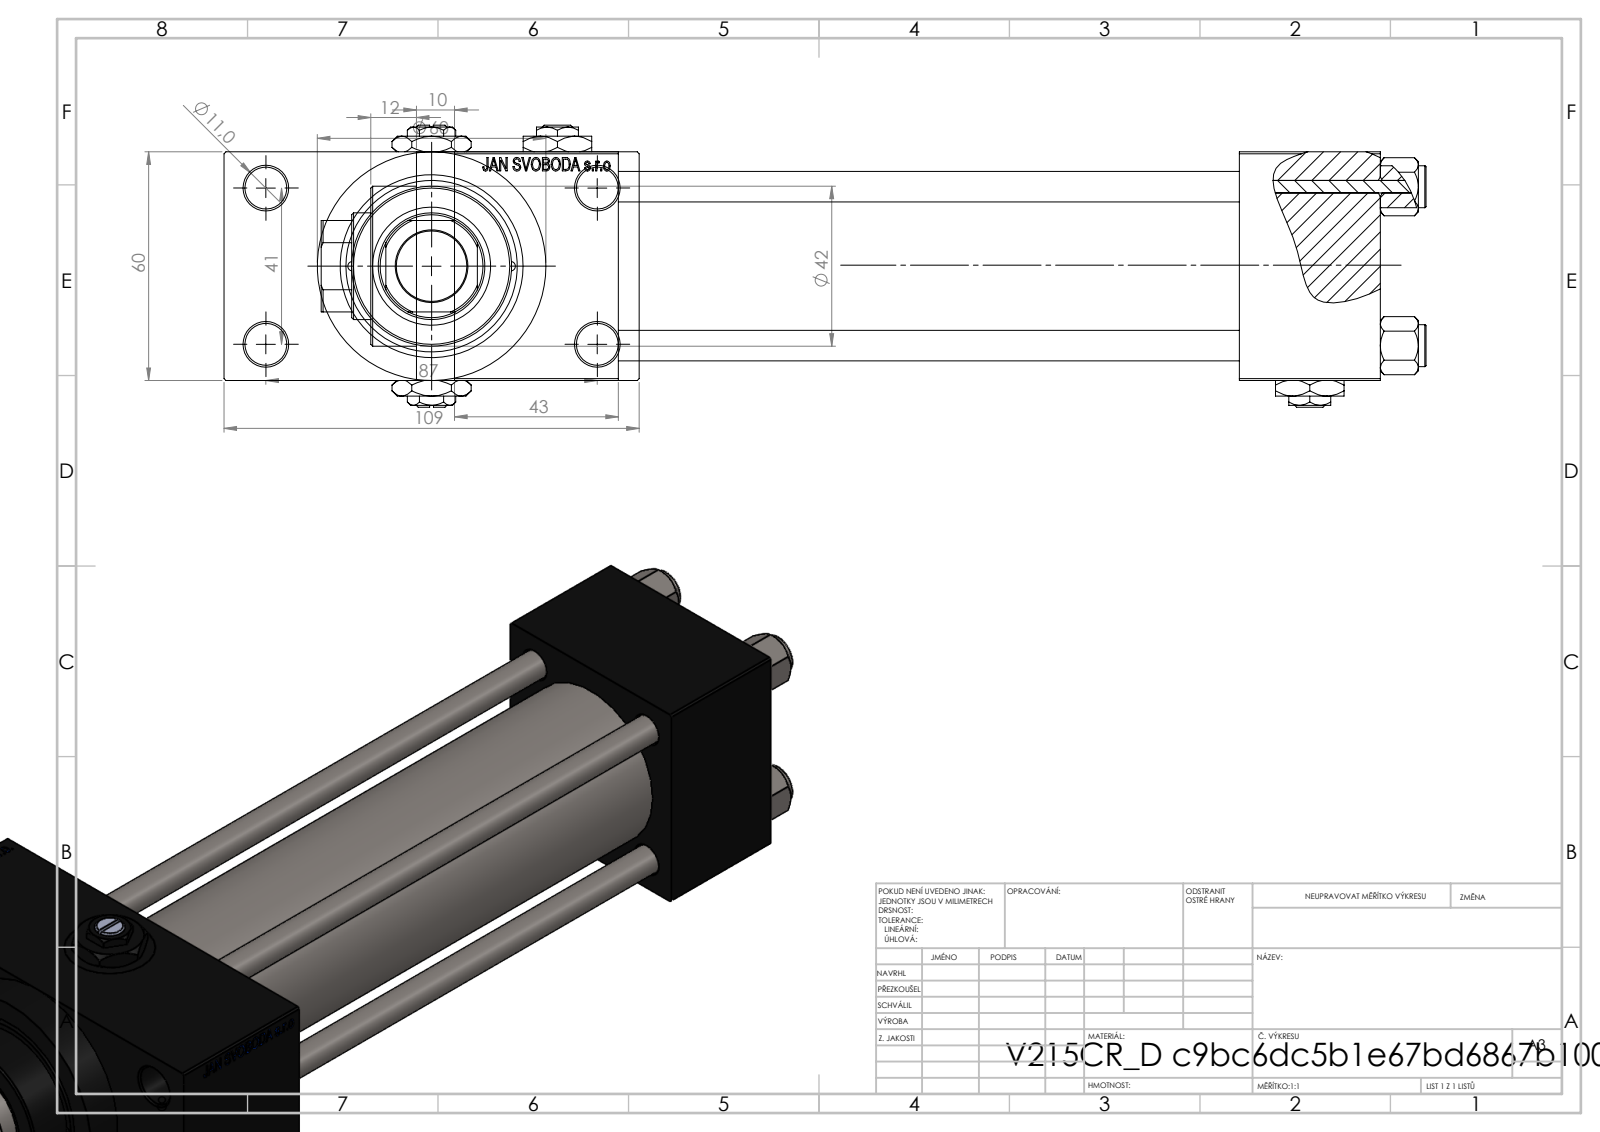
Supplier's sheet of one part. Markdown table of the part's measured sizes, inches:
| quantity | value |
| --- | --- |
| part name | Zatka_pro_OIL_PORT; NUT_M5_D; V215CR_D_TYCINKA; V215CR_D_Body (+2 more) |
| STEP written by | SolidWorks 2019 (CONFIG_CONTROL_DESIGN) |
| units | inches |
| bodies | 13 solids, 1199 faces (546 planar, 93 cylindrical, 560 other) |
| overall size | 11.417 × 4.291 × 2.913 |
| volume | 40.59 in³ |
| surface area | 275.5 in² |
| round holes (diameter × count) | 0.315 × 4, 0.433 × 4, 0.098 × 2, 0.276 × 2, 0.656 × 2, 0.945 × 2, 0.728 × 1, 1.102 × 1, 1.22 × 1, 1.575 × 1, 1.772 × 1 |
| round bosses / shafts (diameter × count) | 0.433 × 4, 2.362 × 1, 1.811 × 1, 1.654 × 1 |
| partial cylindrical surfaces (radius × count) | 0.531 × 1 |
| main face-to-face distances | 2.362, 0.965, 3.327, 6.417, 1.457, 7.874, 9.567, 8.11, 1.693, 4.291 |
| hole center spacings | 0.821, 0.892, 1.161, 1.206, 1.642, 1.832, 1.856, 1.893 |
